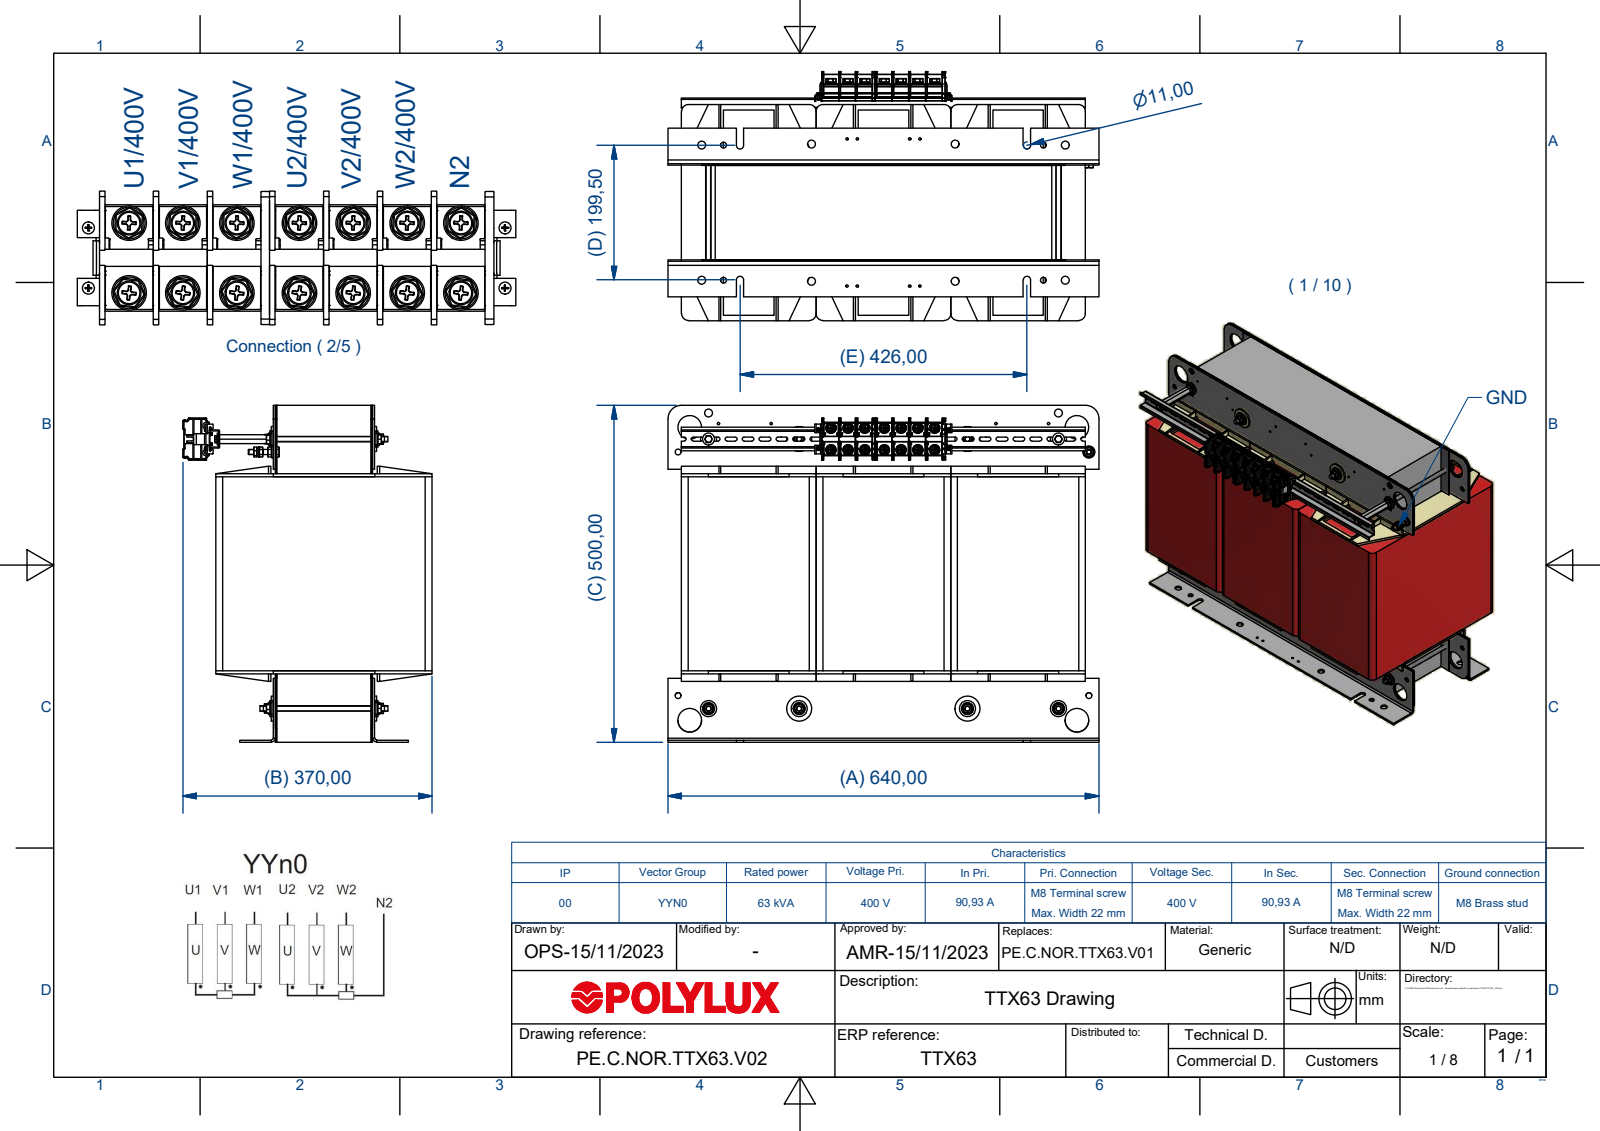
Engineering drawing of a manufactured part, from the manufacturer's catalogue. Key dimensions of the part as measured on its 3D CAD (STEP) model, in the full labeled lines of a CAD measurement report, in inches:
Part name (STEP PRODUCT): TTX63_V02
STEP written by: Autodesk Inventor 2018 (AUTOMOTIVE_DESIGN)
Units: inches
Bodies: 148 solids, 8621 faces (3071 planar, 3263 cylindrical, 2287 other)
Overall size (bounding box): 25.197 × 19.685 × 14.157
Volume: 4 417 in³ · Surface area: 8 590 in²
Round holes (diameter × count): ⌀0.331 ×23, ⌀0.335 ×23, ⌀0.472 ×22, ⌀0.177 ×20, ⌀0.138 ×18, ⌀0.315 ×14, ⌀0.394 ×14, ⌀0.354 ×10, ⌀0.453 ×10, ⌀0.262 ×9, ⌀1.378 ×6, ⌀0.443 ×4
Round bosses / shafts (diameter × count): ⌀0.63 ×23, ⌀0.583 ×22, ⌀0.398 ×14, ⌀0.309 ×14, ⌀0.315 ×9, ⌀0.154 ×4, ⌀0.118 ×4, ⌀0.35 ×2
Partial cylindrical surfaces — rounded edges, fillets, slot ends (radius × count): R0.006 ×1173, R0.02 ×120, R0.039 ×74, R0.014 ×56, R0.118 ×50, R0.061 ×44, R0.197 ×20, R0.01 ×14
Main face-to-face distances: 7.874, 0.157, 5.906, 15.748, 6.063, 5.591, 0.079, 1.811, 1.969, 4.094
Hole centre spacings: 7.874, 13.131, 8.11, 3.071, 3.733, 9.843, 16.621, 0.591
